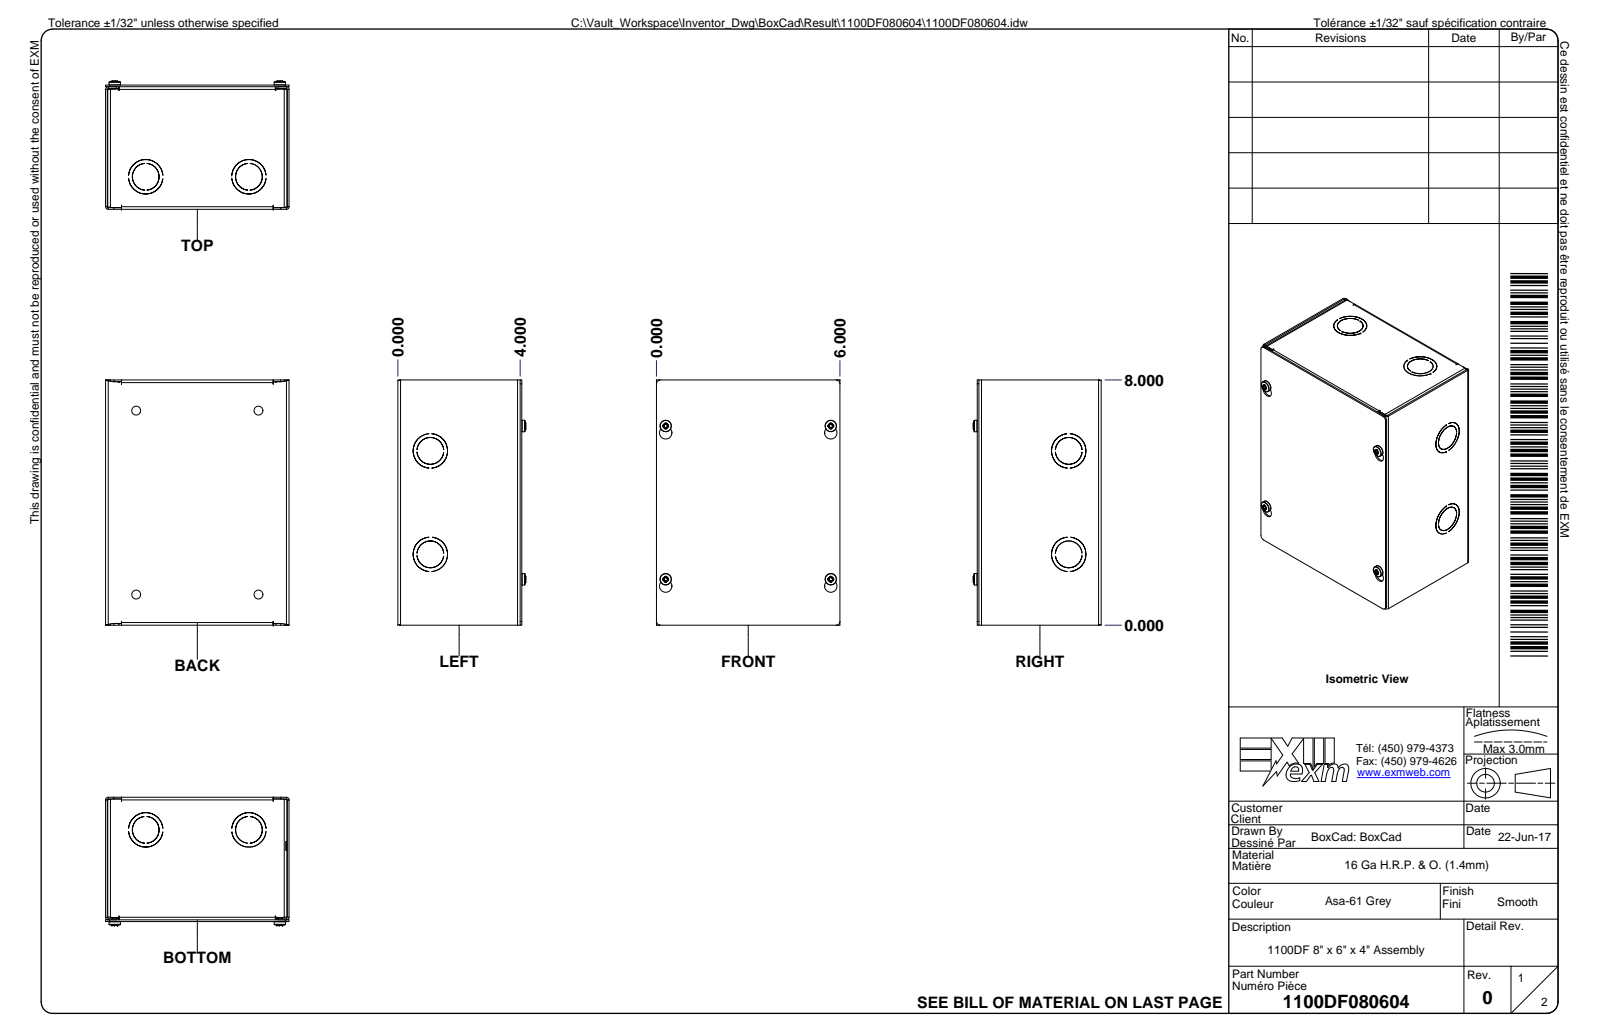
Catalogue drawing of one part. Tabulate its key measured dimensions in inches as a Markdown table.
| quantity | value |
| --- | --- |
| part name | 1100DF080604; 1100DF080604B; 1100DF080604B-P; 1100DF080604C (+5 more) |
| STEP written by | Autodesk Inventor 2024 (AUTOMOTIVE_DESIGN) |
| units | inches |
| bodies | 8 solids, 3389 faces (2082 planar, 415 cylindrical, 892 other) |
| overall size | 8 × 6 × 4.183 |
| volume | 12.2 in³ |
| surface area | 462 in² |
| round holes (diameter × count) | 0.165 × 4, 0.29 × 4, 0.406 × 4, 0.875 × 4, 1.125 × 4, 0.033 × 2, 0.177 × 2, 0.043 × 1, 0.312 × 1, 1.063 × 1 |
| round bosses / shafts (diameter × count) | 1.125 × 4, 0.875 × 4, 0.374 × 4, 0.03 × 2, 1.25 × 1, 1.142 × 1, 0.25 × 1, 0.051 × 1 |
| partial cylindrical surfaces (radius × count) | 0.004 × 28, 0.031 × 14, 0.086 × 14, 0.059 × 12, 0.11 × 12, 0.062 × 4, 0.094 × 4, 0.117 × 4 |
| main face-to-face distances | 0.055, 5.945, 3.945, 0.053, 7.945, 4, 4.053, 3.998, 6, 5.89 |
| hole center spacings | 0.222, 0.86, 4.726, 5, 5.4, 5.405, 5.544, 7.235 |
